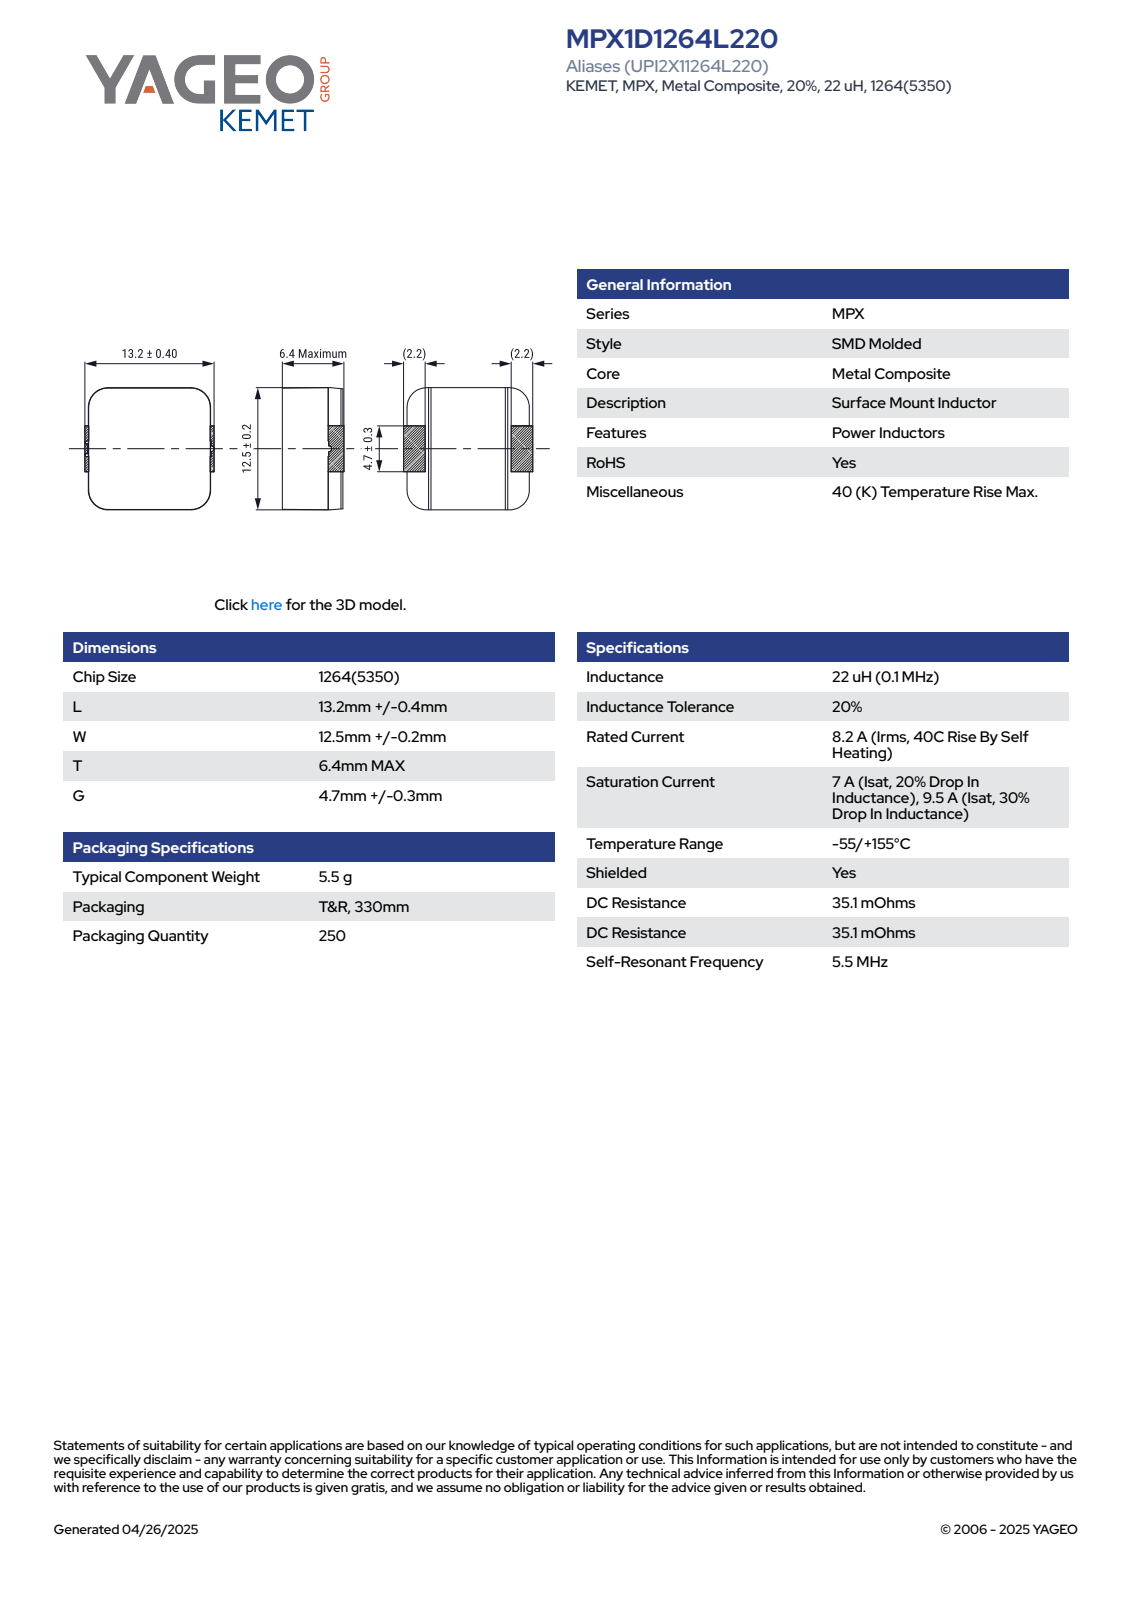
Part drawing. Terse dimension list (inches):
name: MPX1D1264(4_7)(KEMET)
written by: SolidWorks 2018 (AUTOMOTIVE_DESIGN)
unit: in
bodies: 1 solid, 122 faces (105 planar, 17 cylindrical, 0 other)
size: 0.535 × 0.5 × 0.254
volume: 0.06 in³; area: 0.99 in²
rounds: 4× R0.01, 4× R0.077, 4× R0.079, 3× R0.006
face distances: 0.252, 0.244, 0.254, 0.525, 0.043, 0.515, 0.535, 0.051, 0.054, 0.201
